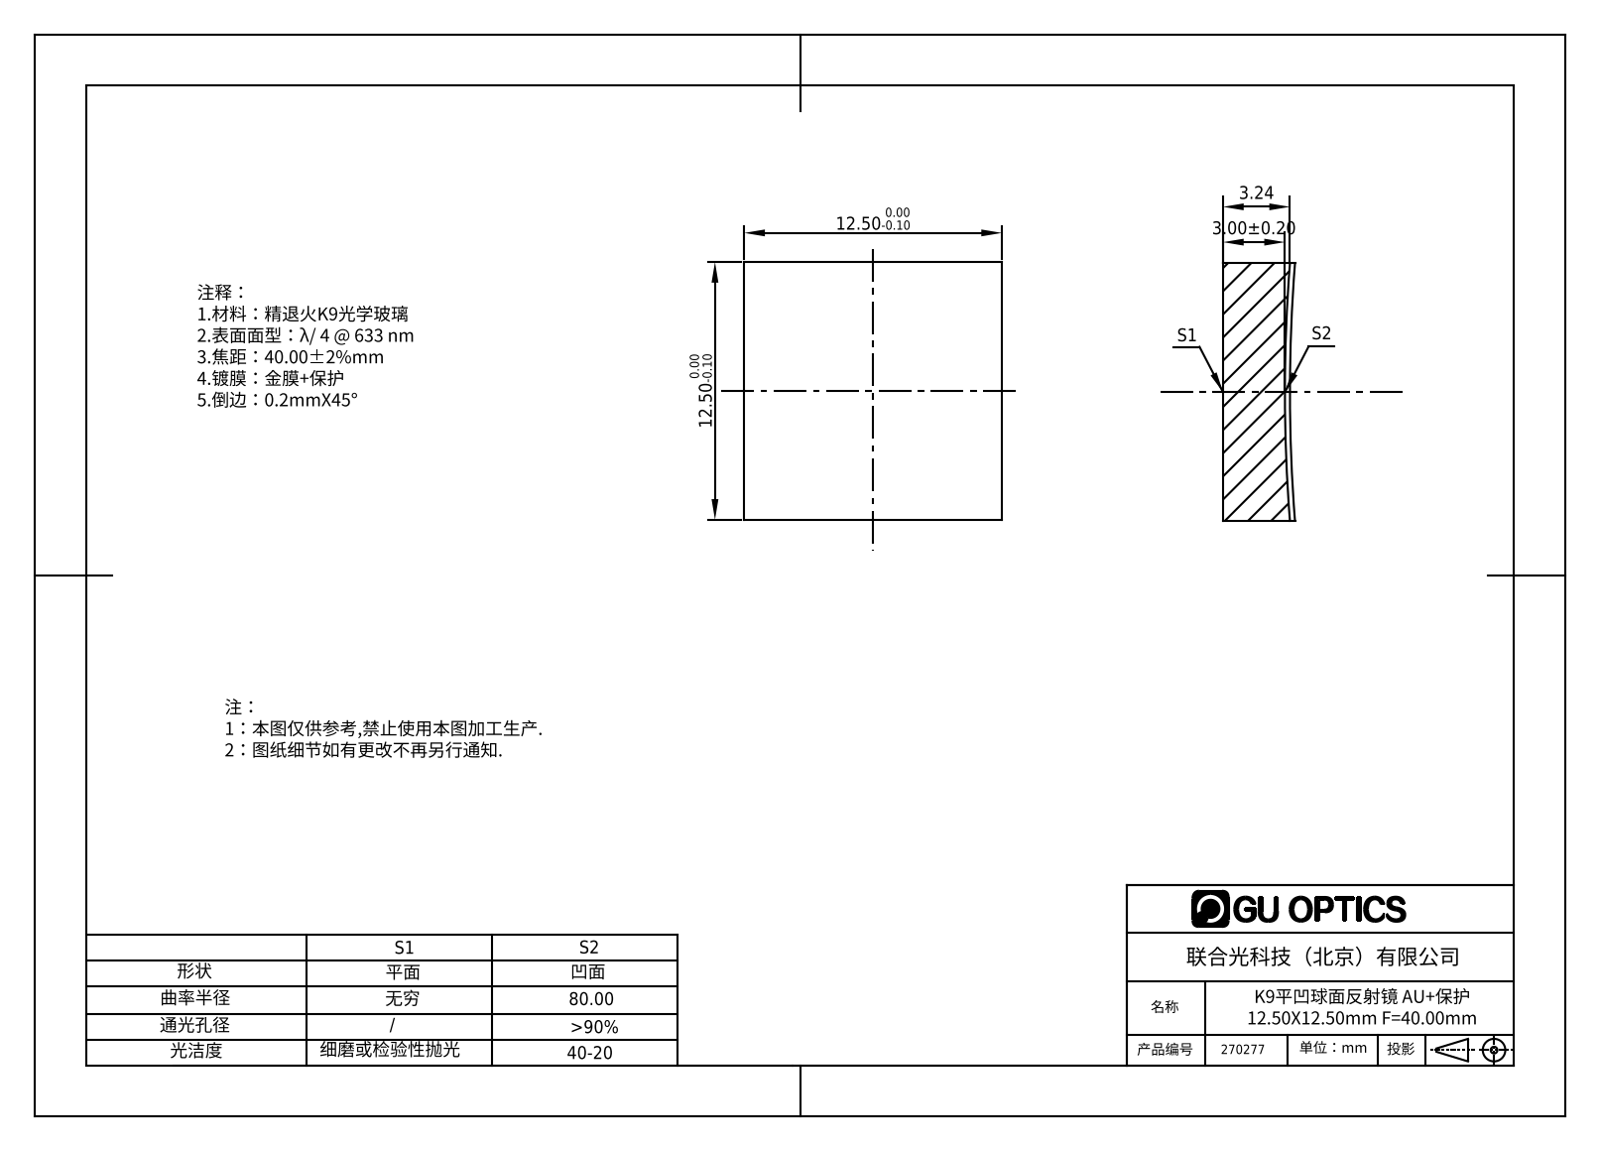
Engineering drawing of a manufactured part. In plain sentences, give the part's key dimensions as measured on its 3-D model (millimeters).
The part is named "270017". Its 3-D file was written by "SolidWorks 2019 (AUTOMOTIVE_DESIGN)". It is 1 solid with 7 faces: 5 planar, 0 cylindrical and 2 other. Overall it measures 12.5 by 12.5 by 3.49 millimeters. Its volume is 494 cubic millimeters and its surface area 479 square millimeters. The main face-to-face distances are 12.5.
